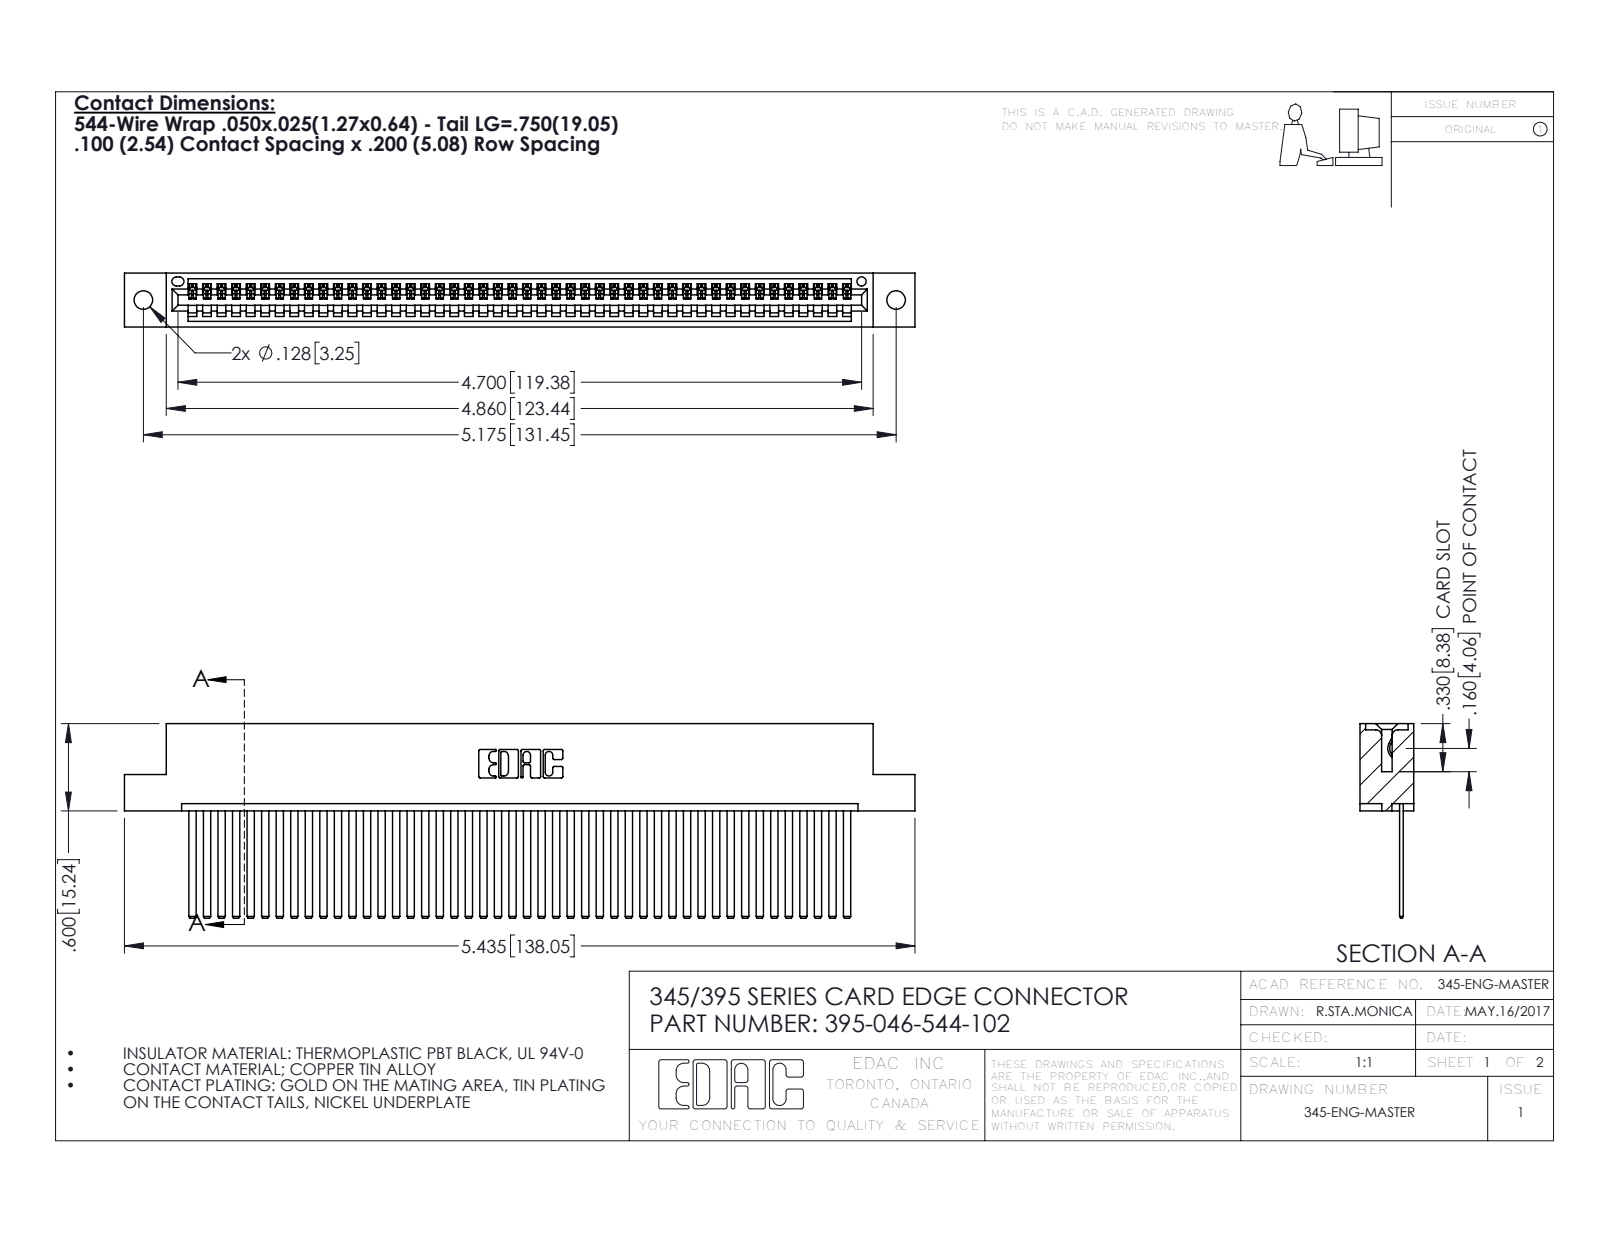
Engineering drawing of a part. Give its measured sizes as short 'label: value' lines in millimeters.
name: 395-046-544-102; 345 Part_Flush Mounting Lugs - 0.128 Dia; 345-292-001_345-293-144
written by: SolidWorks 2016 (CONFIG_CONTROL_DESIGN)
unit: mm
bodies: 47 solids, 2518 faces (1736 planar, 782 cylindrical, 0 other)
size: 138 × 34 × 9.4
volume: 13 600 mm³; area: 19 510 mm²
holes: 2× ⌀3.3, 1× ⌀1.6
rounds: 92× R0.2, 22× R0.3, 6× R0.2, 6× R0.8, 3× R0.7, 2× R0.8, 2× R1, 1× R0.4
face distances: 1.8, 7.6, 0.6, 2.5, 6.9, 9.4, 5.1, 5.7, 3.8, 1.8
hole spacings: 6.9, 125.5, 131.4
